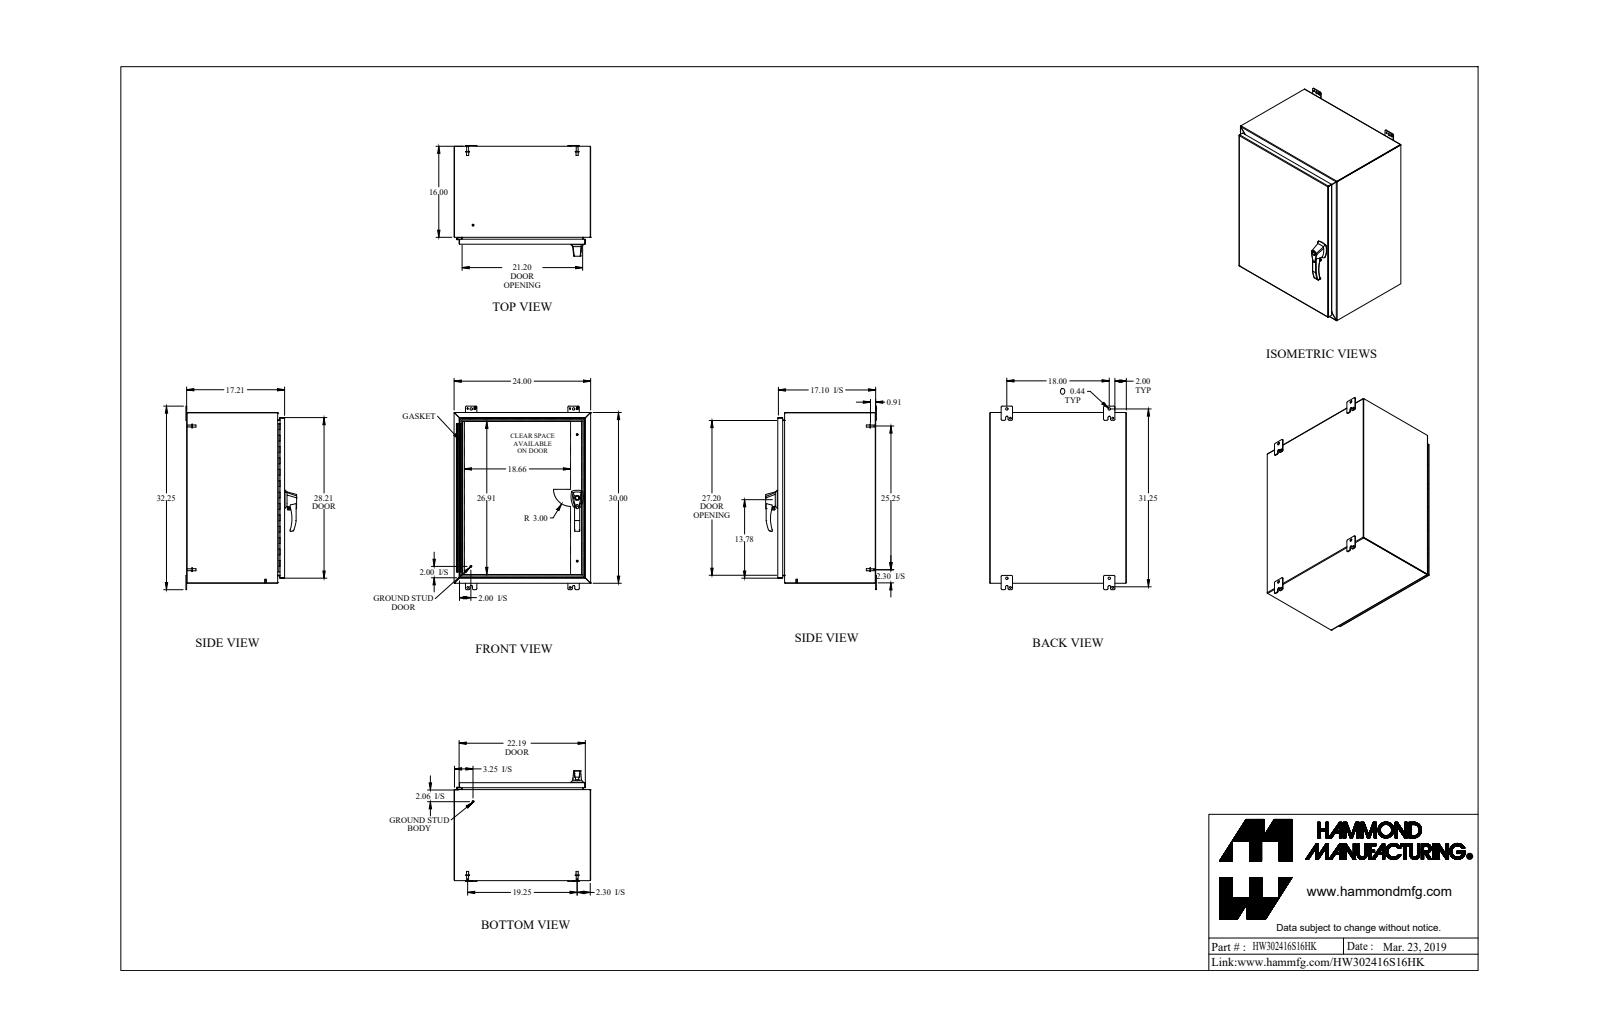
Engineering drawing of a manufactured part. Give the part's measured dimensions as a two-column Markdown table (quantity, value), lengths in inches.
| quantity | value |
| --- | --- |
| part name | HW302416S16HK |
| STEP written by | SolidWorks 2018 (AUTOMOTIVE_DESIGN) |
| units | inches |
| bodies | 44 solids, 1422 faces (675 planar, 603 cylindrical, 144 other) |
| overall size | 32.25 × 24 × 19.45 |
| volume | 281.2 in³ |
| surface area | 7 409 in² |
| round holes (diameter × count) | 0.176 × 6, 0.313 × 5, 0.25 × 3, 0.265 × 3, 0.413 × 3, 0.196 × 2, 0.256 × 2, 0.394 × 2, 0.437 × 2, 0.11 × 1, 0.233 × 1, 0.33 × 1 |
| round bosses / shafts (diameter × count) | 0.375 × 9, 0.25 × 7, 0.156 × 6, 0.65 × 4, 0.332 × 4, 0.313 × 4, 1 × 3, 0.51 × 3 |
| partial cylindrical surfaces (radius × count) | 0.25 × 27, 0.188 × 24, 0.036 × 18, 0.108 × 18, 0.06 × 12, 0.125 × 9, 0.045 × 8, 0.218 × 8 |
| main face-to-face distances | 0.072, 23.928, 29.928, 0.072, 17.138, 17.066, 17.138, 17.21, 23.856, 24 |
| hole center spacings | 1.11, 11.118, 11.119, 22.237, 1.338, 9.78, 10.563, 10.565 |
